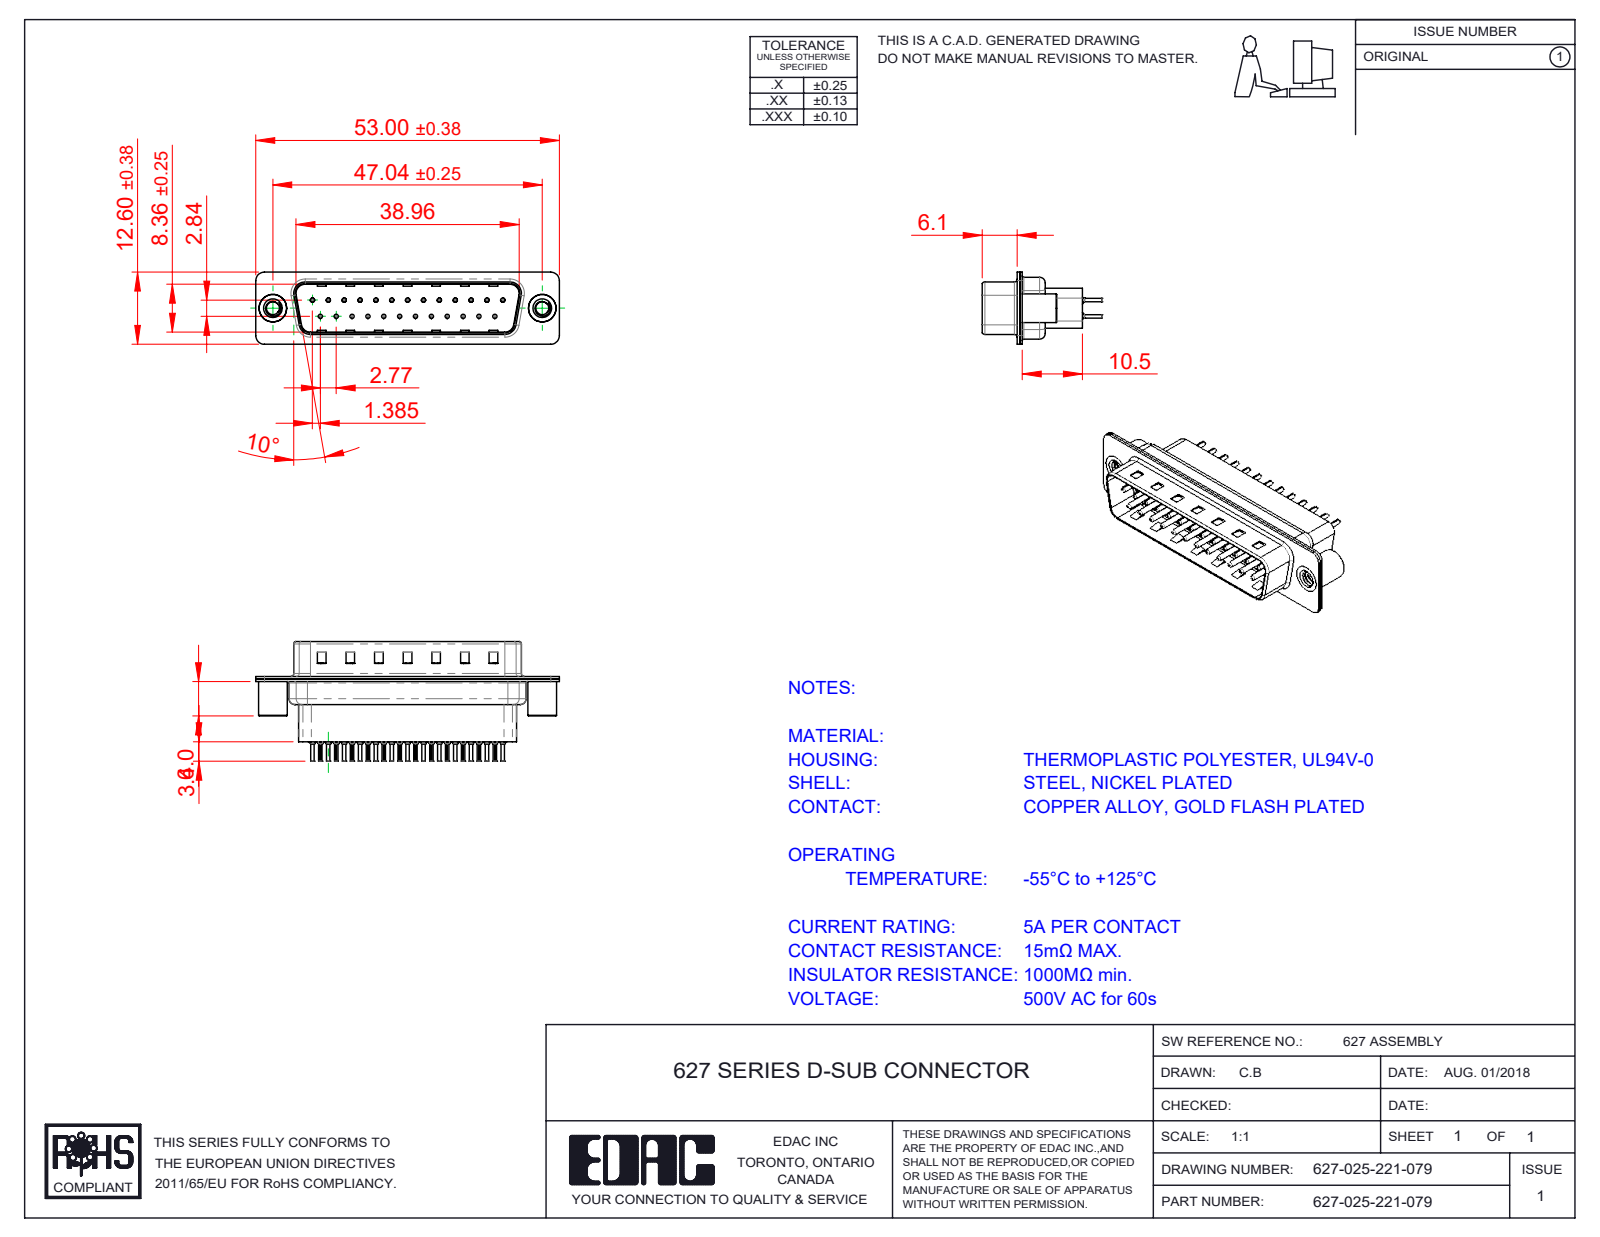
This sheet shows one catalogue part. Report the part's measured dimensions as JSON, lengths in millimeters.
{"part_name": "627 Shell Front_25 Contacts; 627 Shell Rear_25 Contacts; 627 Contact Row 1_21H; 627 4-40 Threaded Standoff BS (+3 more)", "step_written_by": "SolidWorks 2020 (CONFIG_CONTROL_DESIGN)", "units": "millimeters", "bodies": {"solids": 30, "faces": 2848, "planar": 771, "cylindrical": 1082, "other": 995}, "overall_size": [53, 20.8, 12.6], "volume_mm3": 3895, "surface_area_mm2": 9968, "round_holes": [[0.2, 25], [0.35, 25], [1.1, 25], [1.6, 25], [2.26, 2], [4, 2], [4.8, 2]], "round_bosses_or_shafts": [[2, 25], [1.5, 25], [0.75, 25], [0.6, 25], [5, 2], [4.9, 2]], "partial_cylinders_radius": [[0.1, 50], [1.5, 16], [2, 12], [0.5, 8], [1.6, 8], [0.25, 4], [0.6, 4], [0.65, 4]], "face_to_face_distances": [0.4, 0.45, 0.82, 9.58, 0.68, 7.68, 1.5, 0.9, 1.08, 8.08], "hole_center_spacings": [3.16, 8.31, 2.77, 5.54, 11.08, 16.62, 5.03, 5.04]}
